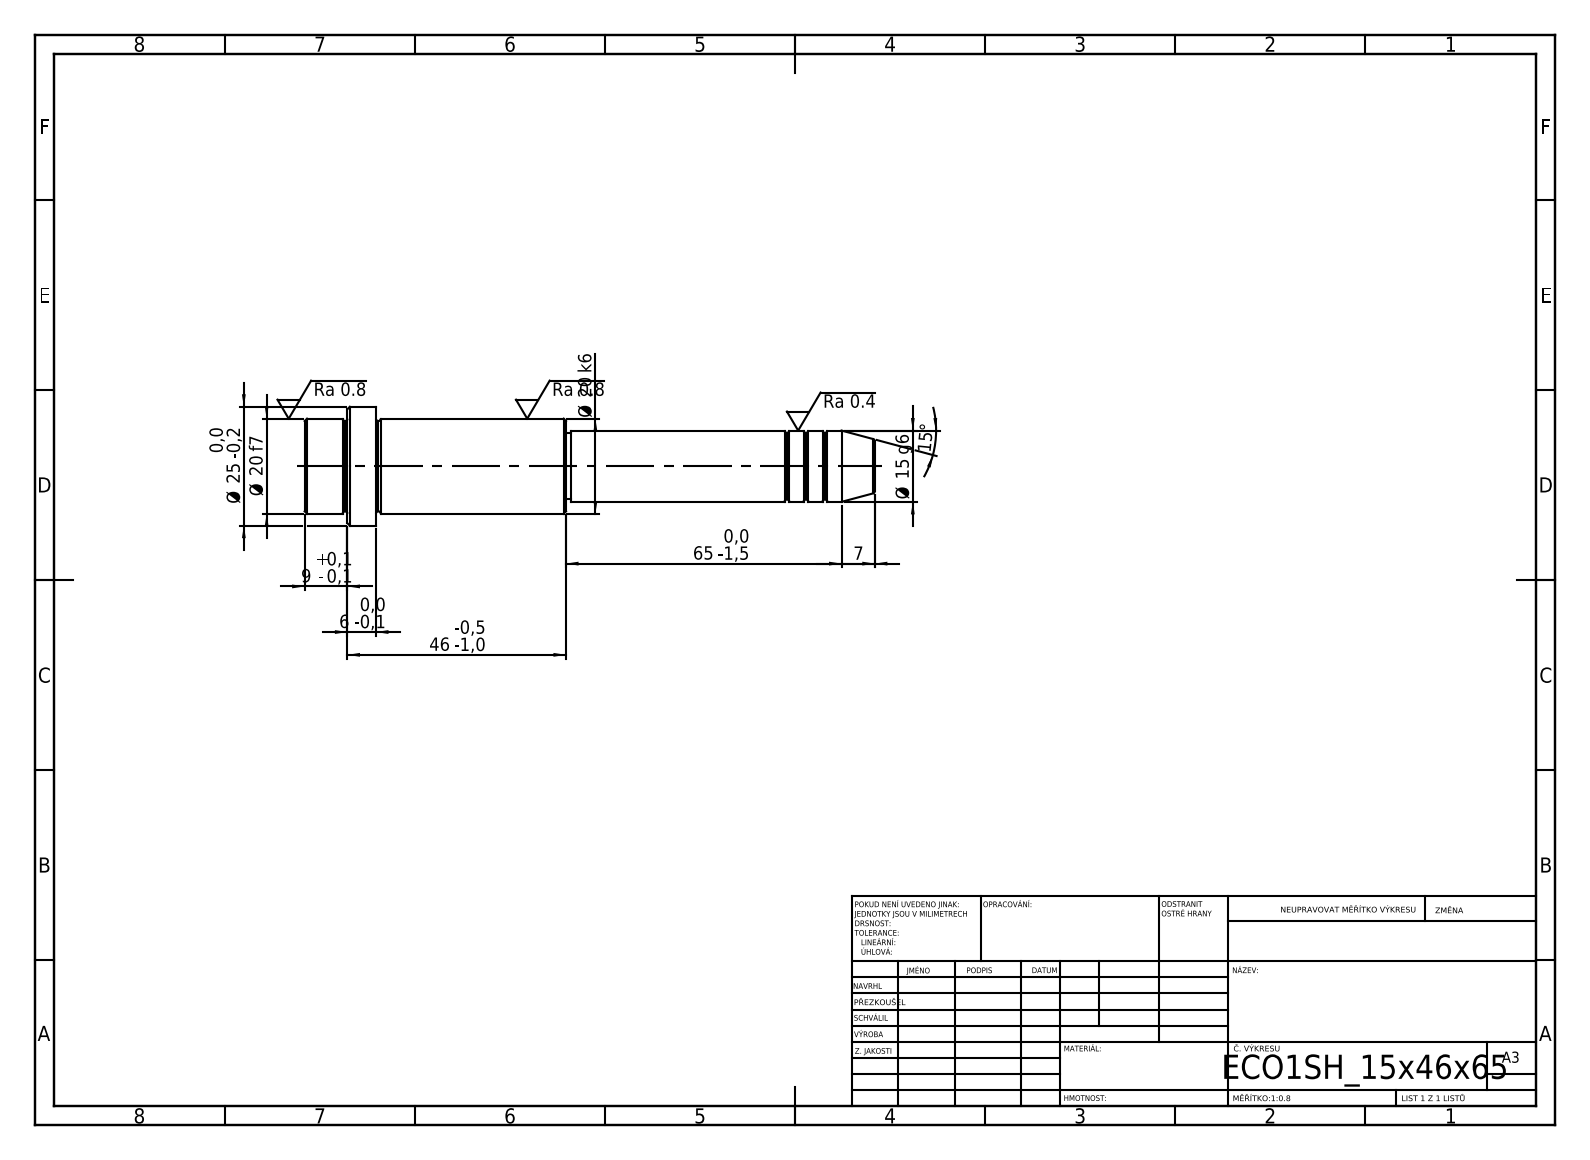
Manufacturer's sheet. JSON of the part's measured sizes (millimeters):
{"step_written_by": "SolidWorks 2019 (CONFIG_CONTROL_DESIGN)", "units": "millimeters", "bodies": {"solids": 1, "faces": 52, "planar": 6, "cylindrical": 16, "other": 30}, "overall_size": [120, 25, 25], "volume_mm3": 29391, "surface_area_mm2": 7601, "round_bosses_or_shafts": [[25, 1], [20, 1], [15, 1], [14, 1]], "face_to_face_distances": [15, 6, 9, 40, 46, 55, 65, 105, 111, 120]}
